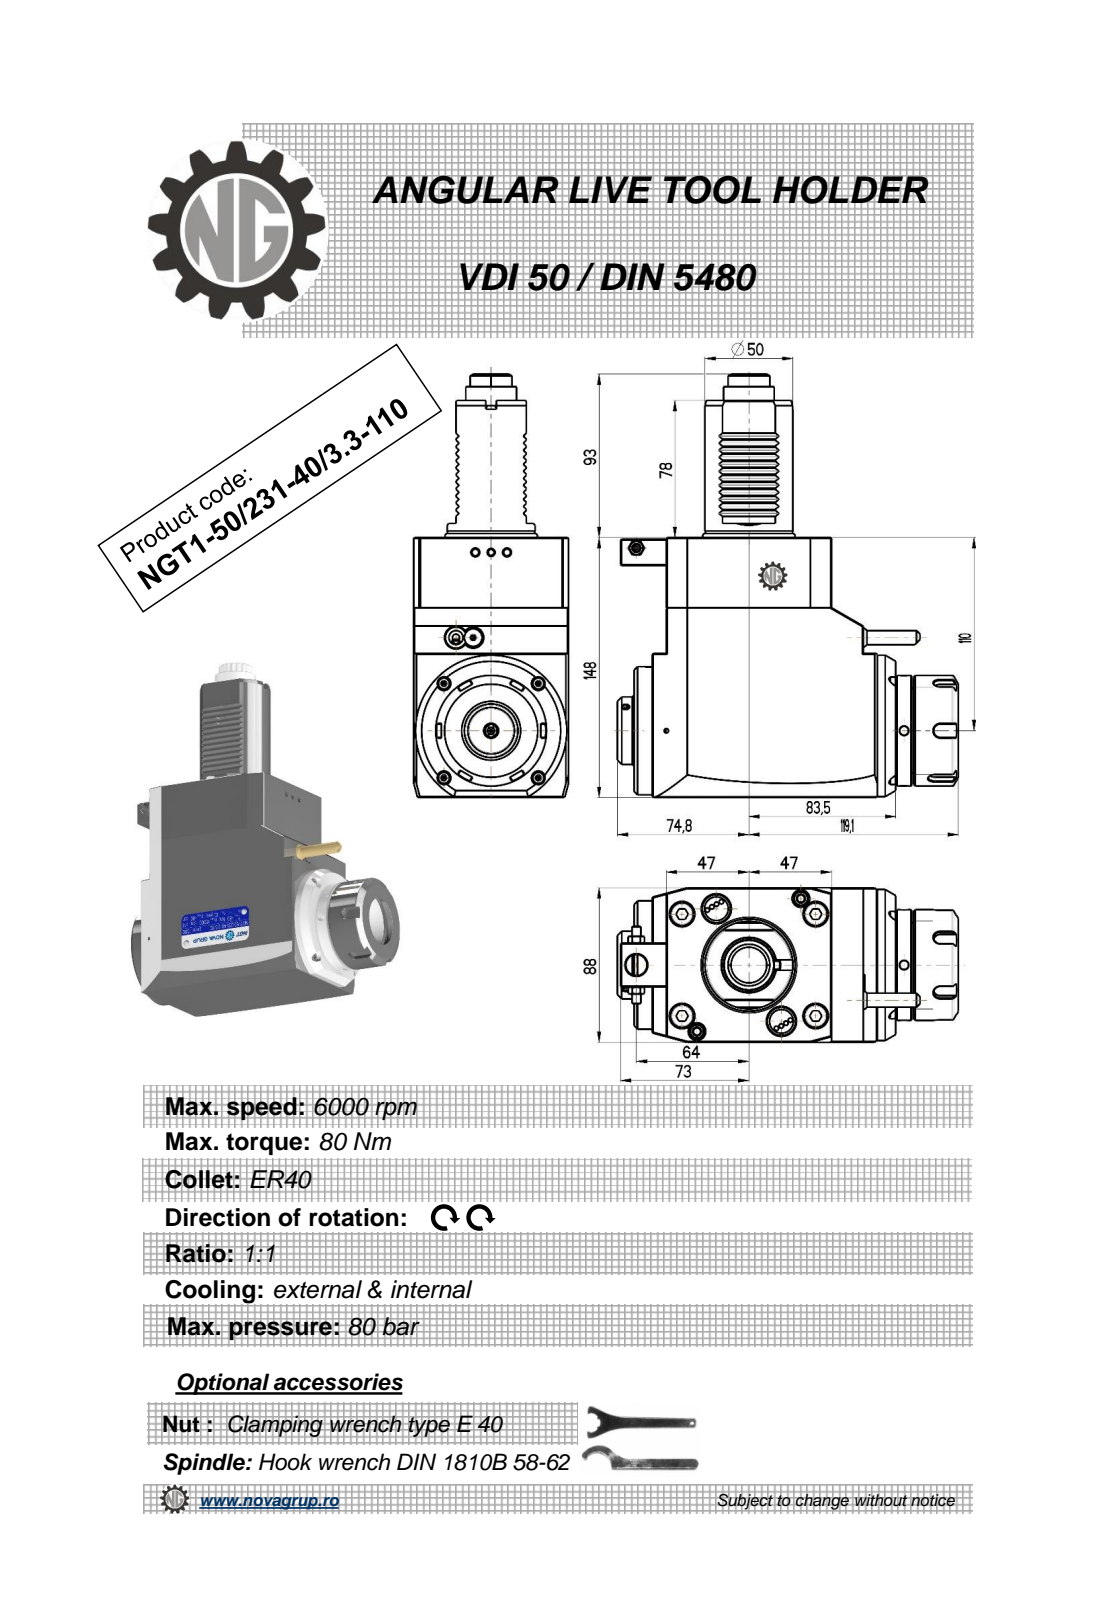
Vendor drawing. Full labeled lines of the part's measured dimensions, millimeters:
Part name (STEP PRODUCT): NGT1_50_231_40_3_3_110
STEP written by: PRO/ENGINEER BY PARAMETRIC TECHNOLOGY CORPORATION, 2010280 (CONFIG_CONTROL_DESIGN)
Units: millimetres
Bodies: 1 solid, 582 faces (248 planar, 177 cylindrical, 157 other)
Overall size (bounding box): 241 × 193.9 × 88
Volume: 1 849 000 mm³ · Surface area: 116 143 mm²
Round holes (diameter × count): ⌀5 ×3, ⌀3 ×1, ⌀4.2 ×1, ⌀9.5 ×1, ⌀12 ×1, ⌀33.5 ×1
Round bosses / shafts (diameter × count): ⌀86 ×1, ⌀73 ×1, ⌀63 ×1, ⌀51 ×1, ⌀50 ×1, ⌀40 ×1, ⌀38.5 ×1, ⌀28.8 ×1
Partial cylindrical surfaces — rounded edges, fillets, slot ends (radius × count): R3.04 ×36, R0.3 ×24, R0.26 ×12, R0.2 ×6, R3.75 ×5, R10.56 ×1, R11.88 ×1, R17.5 ×1
Main face-to-face distances: 88, 148, 94, 8, 120, 36.5, 130.5, 18.3, 112.3, 148.8
Hole centre spacings: 52.46, 56.65, 101.5, 152.25, 184.38
